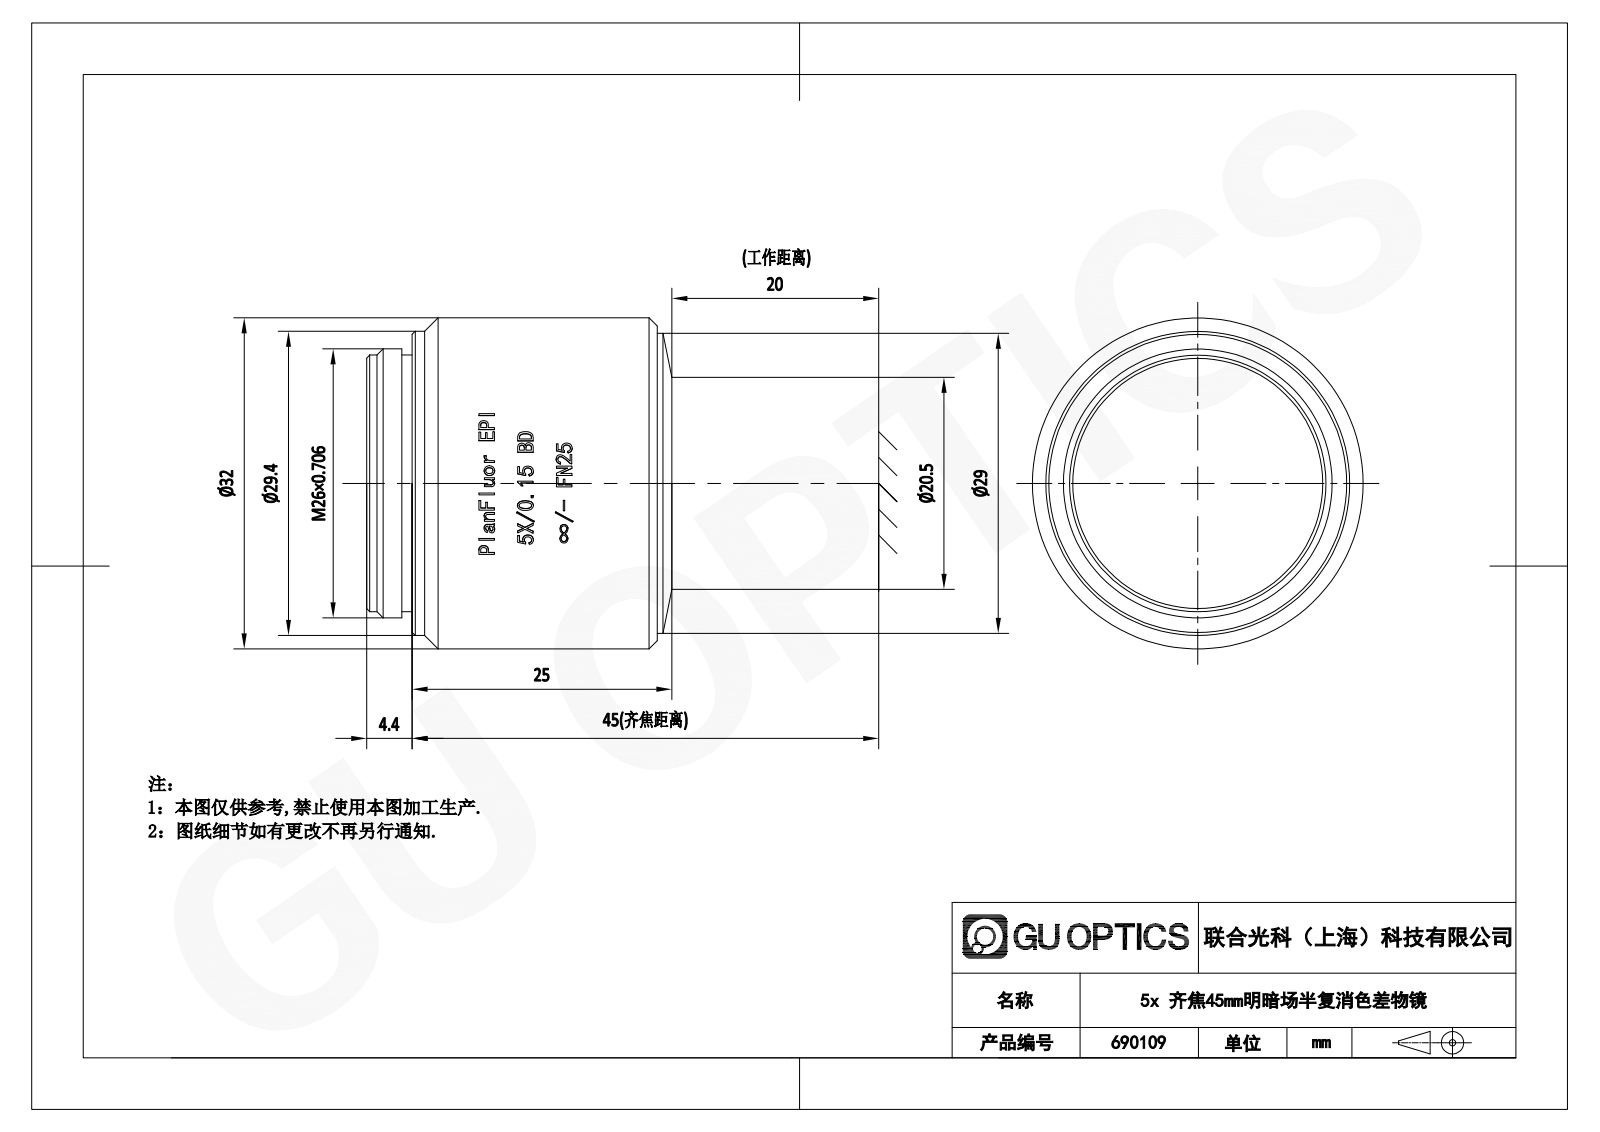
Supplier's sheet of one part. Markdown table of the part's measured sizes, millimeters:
| quantity | value |
| --- | --- |
| part name | 690109 |
| STEP written by | SolidWorks 2020 (CONFIG_CONTROL_DESIGN) |
| units | millimeters |
| bodies | 1 solid, 333 faces (150 planar, 50 cylindrical, 133 other) |
| overall size | 32.05 × 32 × 29.51 |
| volume | 21 795 mm³ |
| surface area | 4 308 mm² |
| round bosses / shafts (diameter × count) | 32 × 1, 29.4 × 1, 29 × 1, 26 × 1, 24.8 × 1 |
| partial cylindrical surfaces (radius × count) | 16.05 × 1 |
| main face-to-face distances | 29.51, 4.4, 25.11, 28.1, 23.7, 1.41, 3.4, 1, 24.7, 26.11 |
